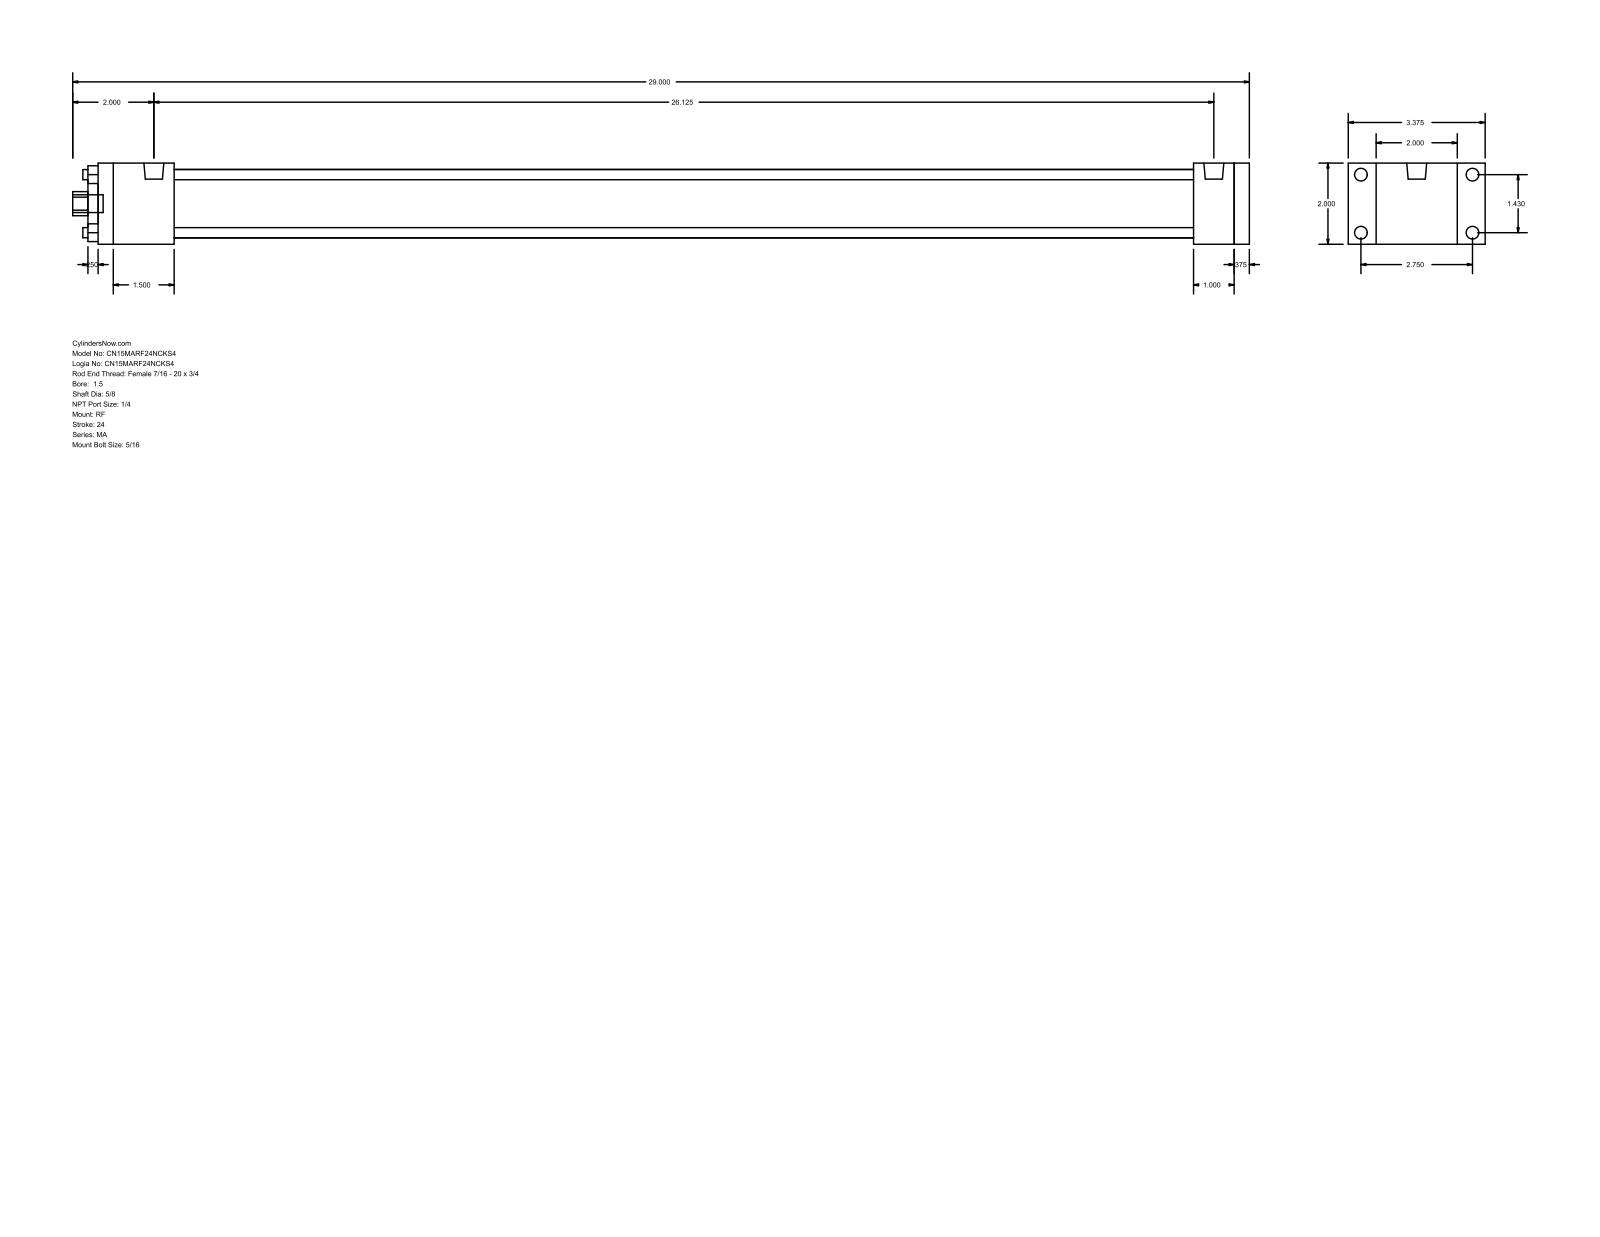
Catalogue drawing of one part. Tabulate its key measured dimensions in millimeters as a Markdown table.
| quantity | value |
| --- | --- |
| part name | MA_RF__0150_0.625 |
| STEP written by | GSSL Pune (CONFIG_CONTROL_DESIGN) |
| units | millimeters |
| bodies | 0 solids, 92 faces (64 planar, 28 cylindrical, 0 other) |
| overall size | 736.6 × 85.72 × 50.8 |
| round holes (diameter × count) | 6.35 × 4, 15.88 × 1, 28.57 × 1, 42.93 × 1 |
| round bosses / shafts (diameter × count) | 7.94 × 8, 12.49 × 2, 11.11 × 1 |
| partial cylindrical surfaces (radius × count) | 7.54 × 1 |
| main face-to-face distances | 50.8, 9.52, 711.2, 720.72, 685.79, 25.41, 34.93, 47.62, 638.17, 663.58 |
| hole center spacings | 25.68, 36.32, 51.36 |
